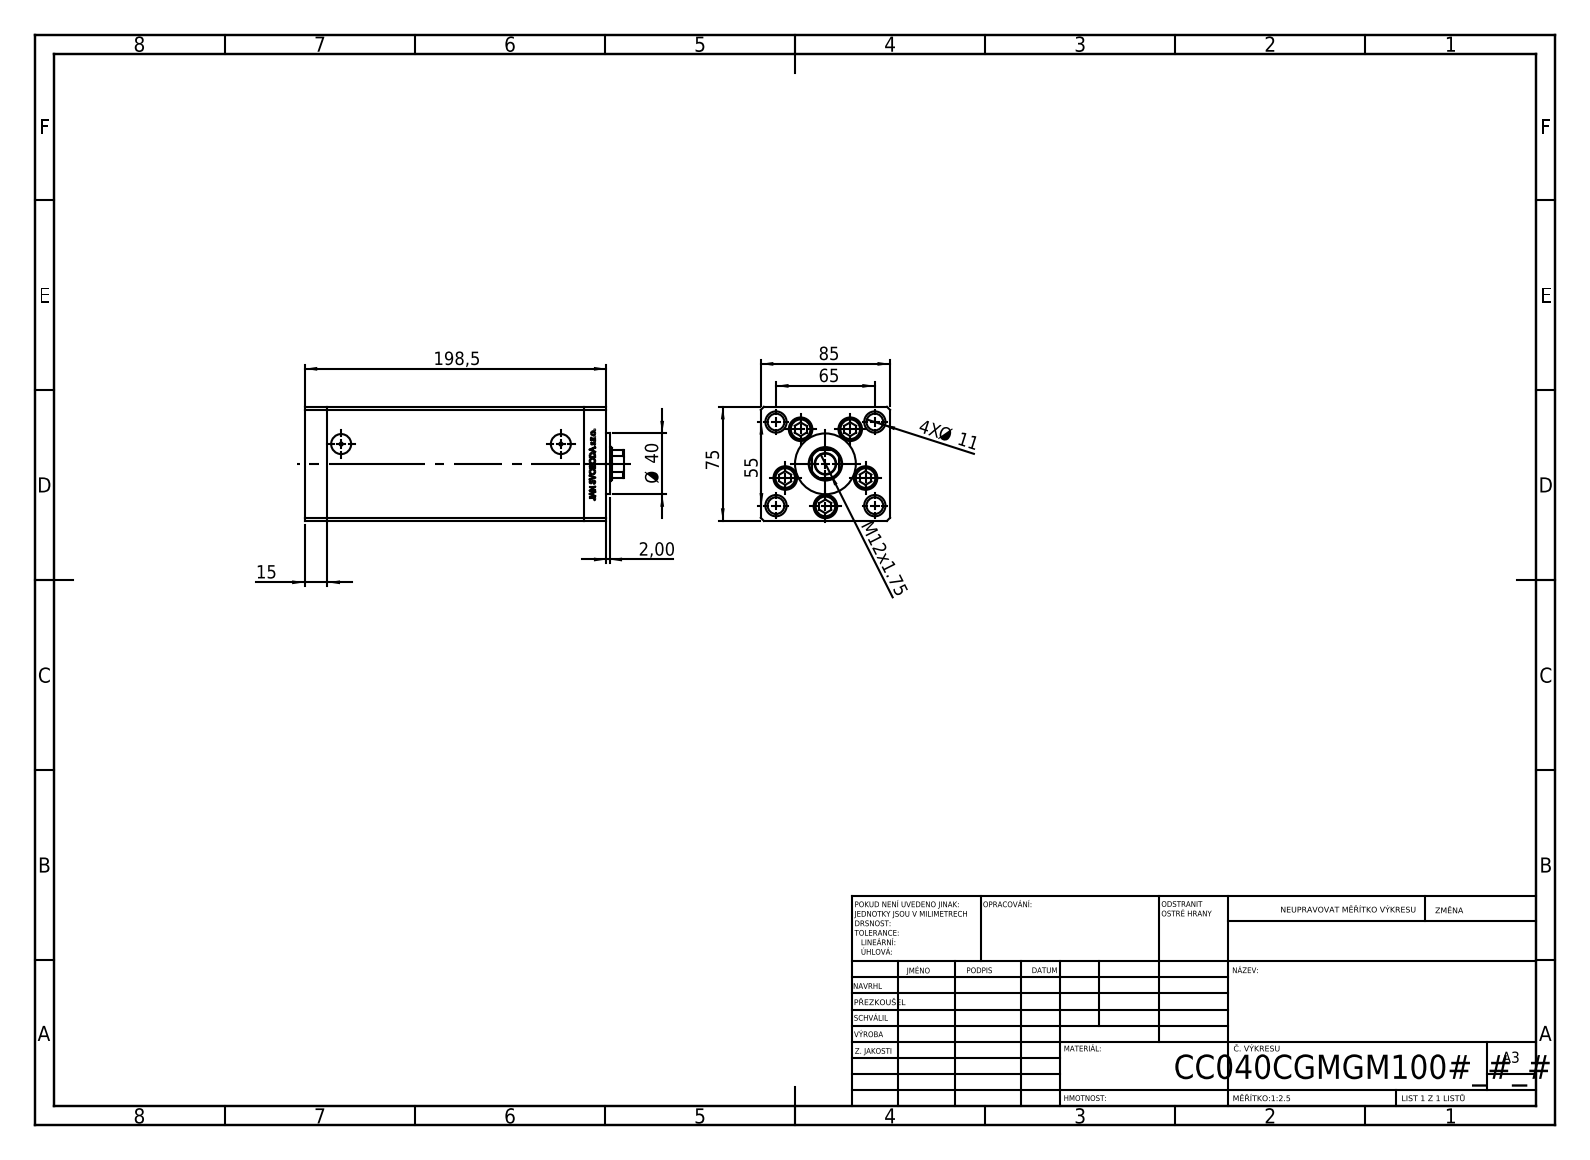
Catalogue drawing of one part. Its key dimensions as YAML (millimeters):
part_name: "V220C_VC_C; ALLEN BOLT; V220C BACK_C; V220C_C MIDDLE (+1 more)"
step_written_by: "SolidWorks 2019 (CONFIG_CONTROL_DESIGN)"
units: millimeters
bodies: {solids: 13, faces: 1175, planar: 546, cylindrical: 167, other: 462}
overall_size: [210, 85, 75]
volume: 1045000
surface_area: 194082
round_holes:
  - {diameter: 11, count: 9}
  - {diameter: 15.5, count: 5}
  - {diameter: 10, count: 4}
  - {diameter: 14, count: 4}
  - {diameter: 2, count: 2}
  - {diameter: 13.16, count: 2}
  - {diameter: 13.5, count: 1}
  - {diameter: 14.5, count: 1}
  - {diameter: 22, count: 1}
round_bosses_or_shafts:
  - {diameter: 8, count: 5}
  - {diameter: 14.5, count: 4}
  - {diameter: 40, count: 1}
partial_cylinders:
  - {radius: 0.93, count: 2}
  - {radius: 10.5, count: 1}
face_to_face_distances: [85, 75, 168.5, 15, 183.5, 10.5, 198.5, 34.25, 68.5, 164.25]
hole_center_spacings: [28, 42.57, 16.86, 19.17, 32.33, 32.5, 33.63, 37.33]
